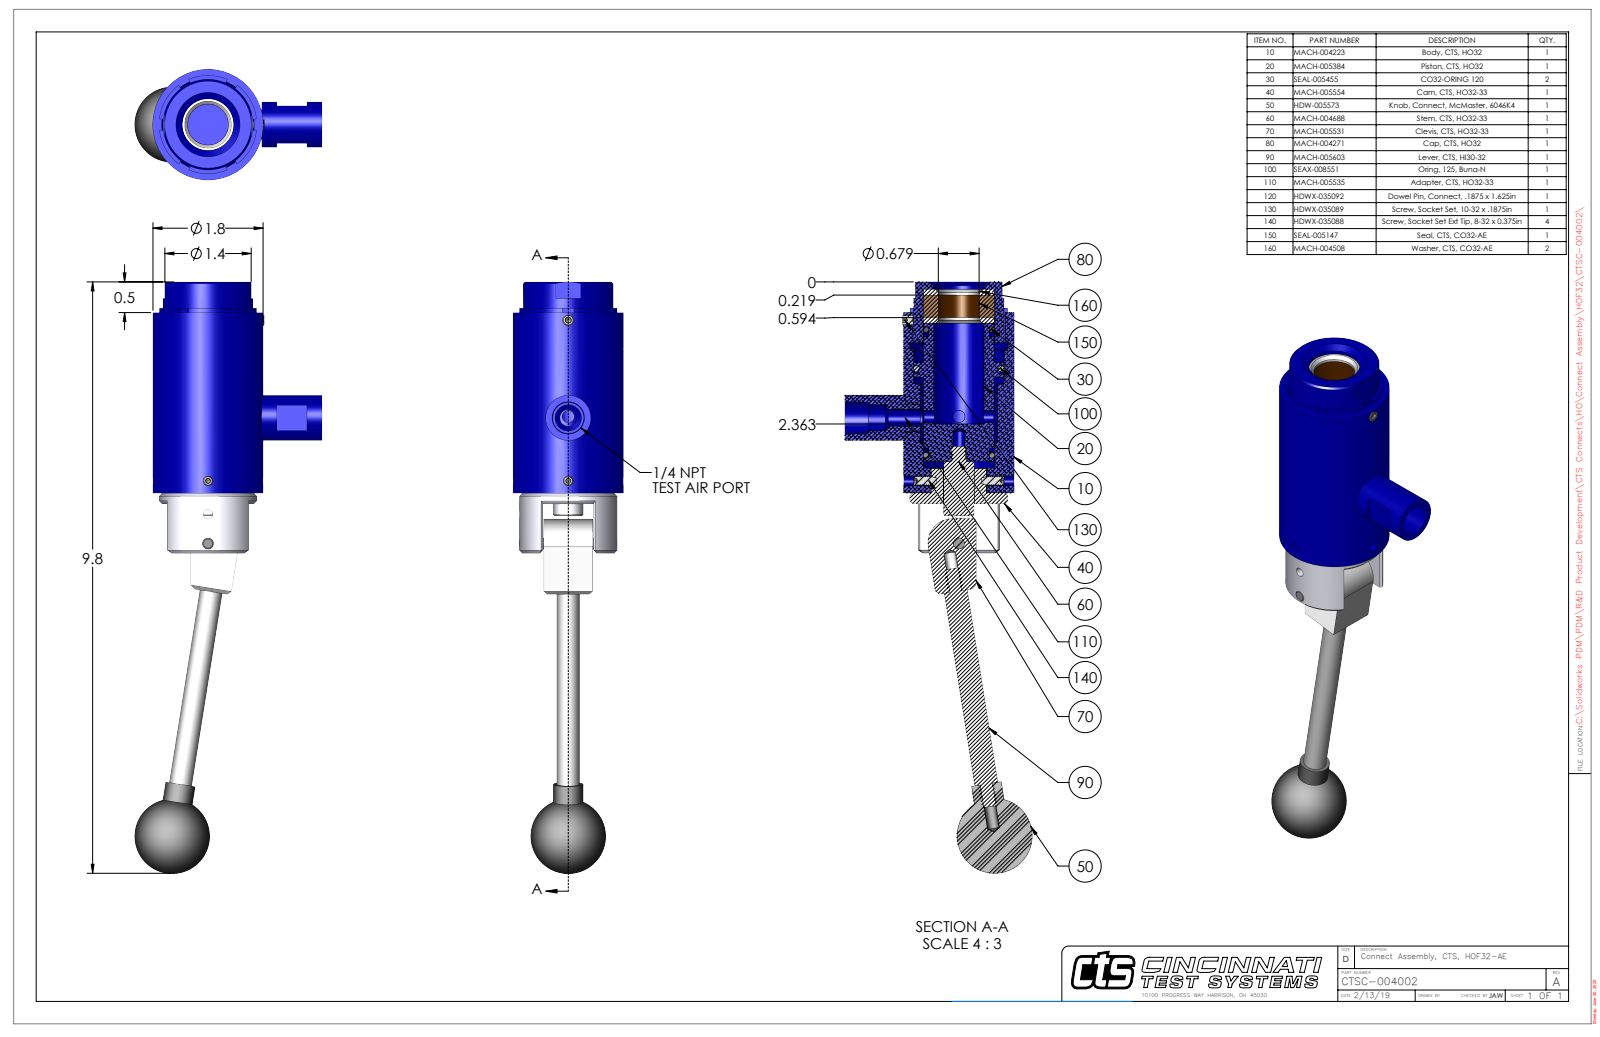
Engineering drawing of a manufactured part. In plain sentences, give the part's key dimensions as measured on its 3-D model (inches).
The part is named "CTSC-004002". Its 3-D file was written by "SolidWorks 2023 (AUTOMOTIVE_DESIGN)". It is 13 solids with 530 faces: 178 planar, 216 cylindrical and 136 other. Overall it measures 9.837 by 3.109 by 1.832 inches. Its volume is 10.8 cubic inches and its surface area 80.02 square inches. Round holes: 3 of diameter 0.201, 2 of diameter 0.159, 1 of diameter 0.094, 1 of diameter 0.189, 1 of diameter 0.19, 1 of diameter 0.203, 1 of diameter 0.203, 1 of diameter 0.281, 1 of diameter 0.438, 1 of diameter 0.453, 1 of diameter 0.516, 1 of diameter 0.529. Round bosses or shafts: 2 of diameter 0.75, 2 of diameter 0.5, 2 of diameter 0.164, 2 of diameter 0.109, 1 of diameter 1.832, 1 of diameter 1.625, 1 of diameter 1.495, 1 of diameter 1.172. Partial cylindrical surfaces (rounded edges, fillets, slot ends): 1 of radius 0.228, 1 of radius 0.4, 1 of radius 0.77, 1 of radius 0.811, 1 of radius 0.825. The main face-to-face distances are 0.094, 0.469, 0.014, 0.826, 3, 0.375, 0.178, 3.094, 3.469, 0.84. The hole center spacings are 0.022, 0.488, 1.128, 1.603, 1.622, 1.625, 2.11, 2.75.
